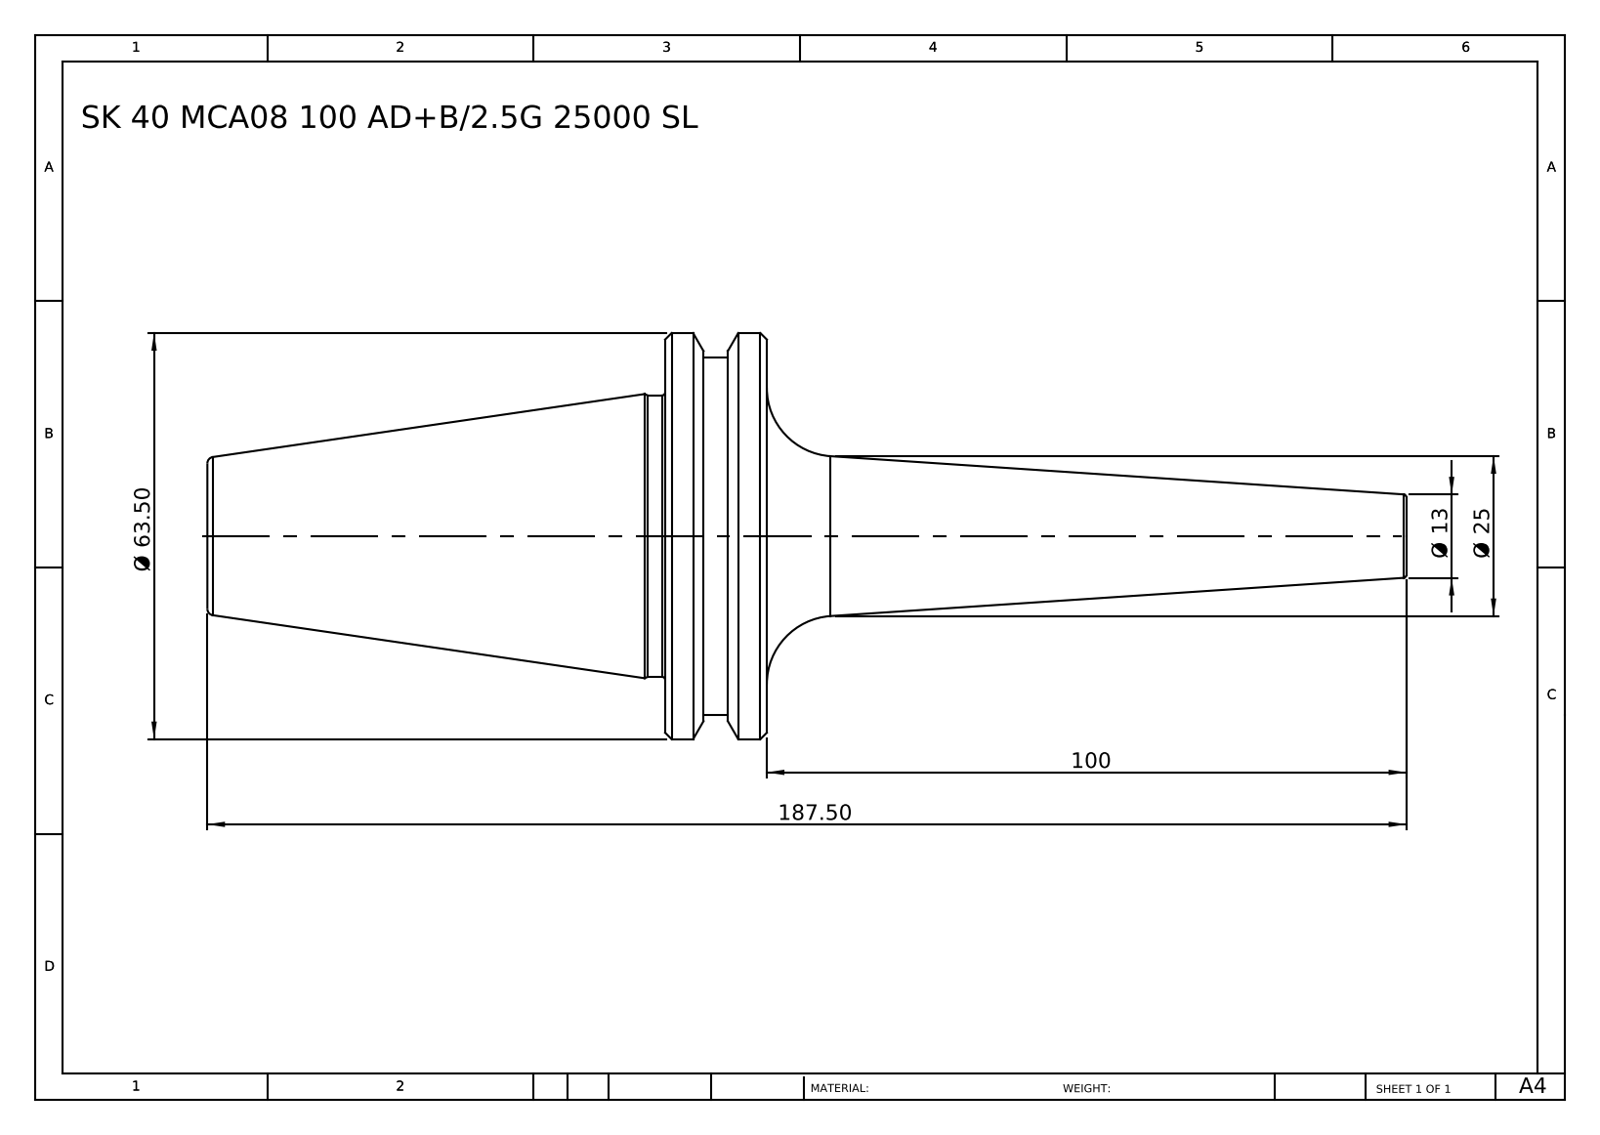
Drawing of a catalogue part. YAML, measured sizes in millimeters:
part_name: "SK 40 MCA08 100 AD+B-2.5G 25000 SL"
step_written_by: "SolidWorks 2014 (CONFIG_CONTROL_DESIGN)"
units: millimeters
bodies: {solids: 1, faces: 36, planar: 6, cylindrical: 8, other: 22}
overall_size: [187.5, 63.5, 63.5]
volume: 150659
surface_area: 22437
round_bosses_or_shafts:
  - {diameter: 63.5, count: 1}
  - {diameter: 56, count: 1}
  - {diameter: 44, count: 1}
face_to_face_distances: [15.9, 87.5, 71.6, 6.1, 9.8, 81.4, 9.9, 3.8, 6, 77.6]
